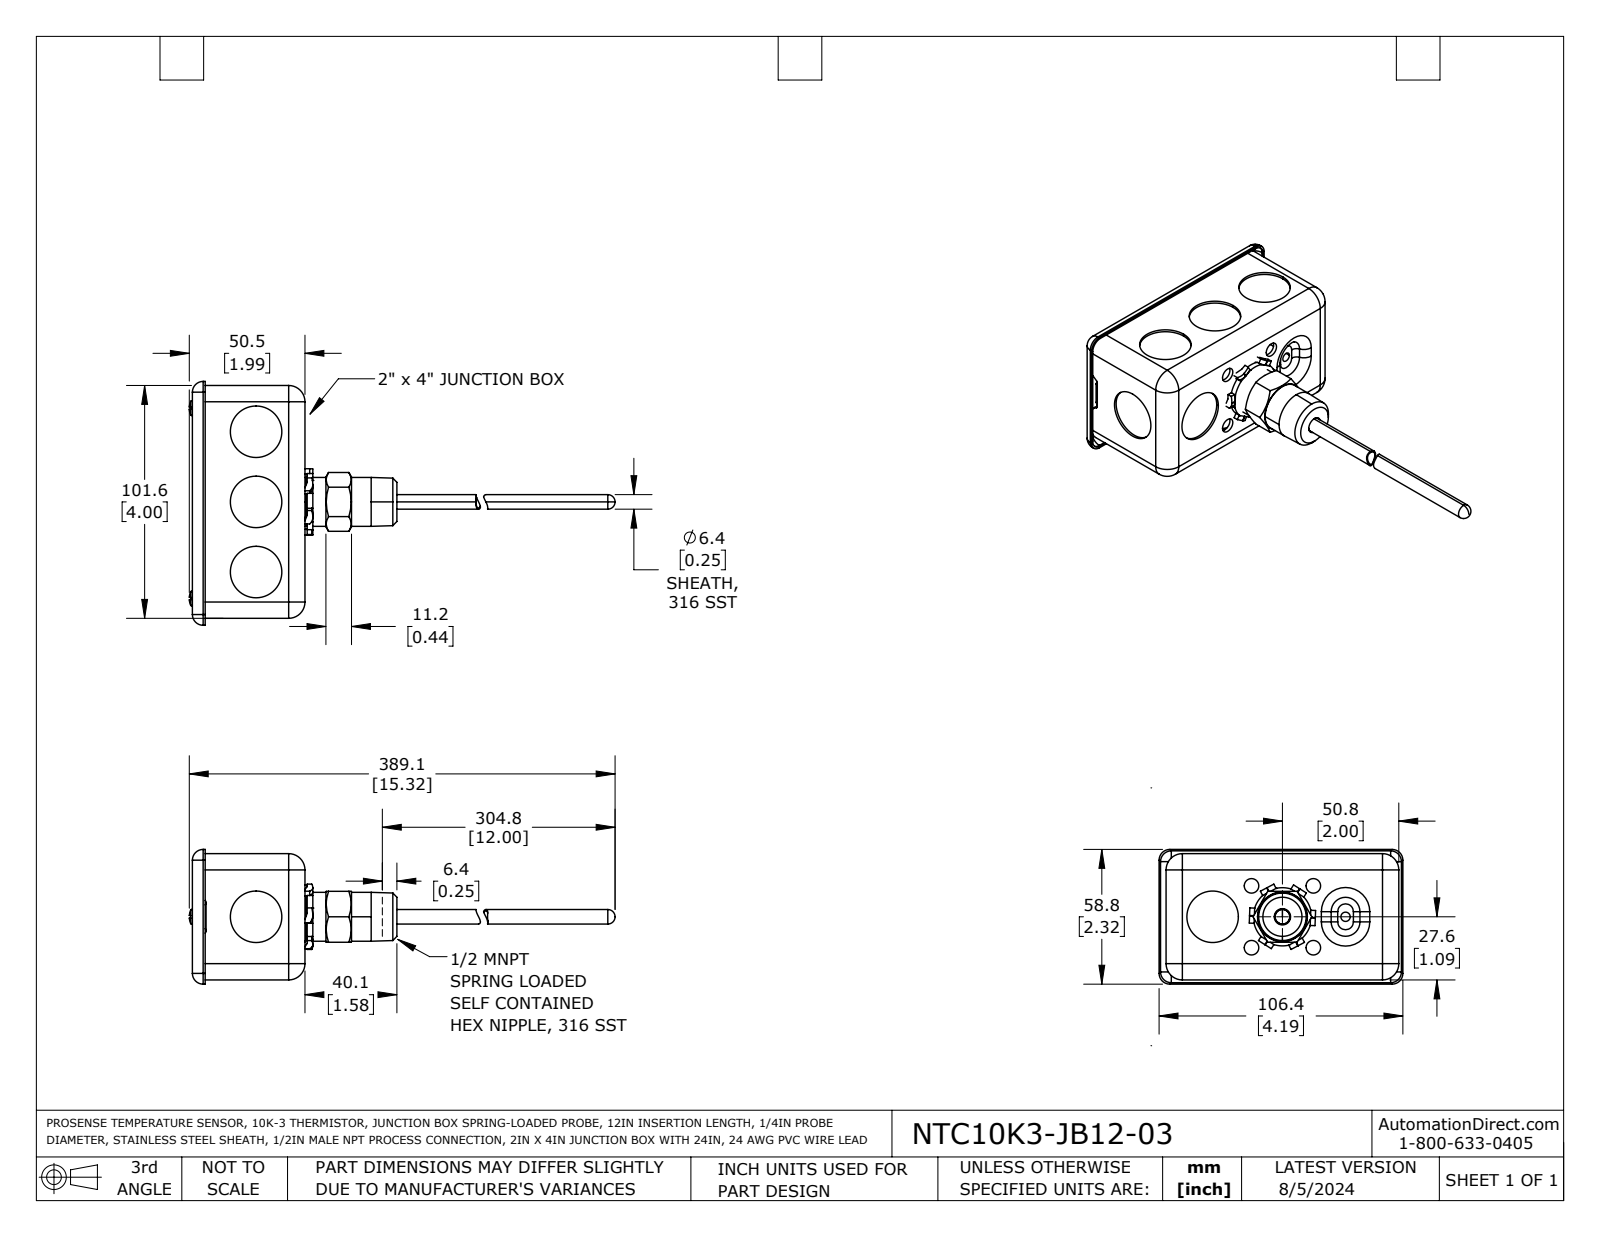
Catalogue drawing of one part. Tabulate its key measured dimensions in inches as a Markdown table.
| quantity | value |
| --- | --- |
| part name | NTC10K3-JB12-03 |
| STEP written by | SolidWorks 2021 (AUTOMOTIVE_DESIGN) |
| units | inches |
| bodies | 5 solids, 366 faces (155 planar, 147 cylindrical, 64 other) |
| overall size | 15.313 × 4.19 × 2.315 |
| volume | 3.194 in³ |
| surface area | 110 in² |
| round holes (diameter × count) | 0.885 × 6, 0.25 × 4, 0.115 × 2, 0.16 × 1, 0.21 × 1, 0.26 × 1, 0.438 × 1, 0.466 × 1 |
| round bosses / shafts (diameter × count) | 0.136 × 2, 0.84 × 1, 0.25 × 1 |
| partial cylindrical surfaces (radius × count) | 0.185 × 16, 0.245 × 8, 0.28 × 8, 0.174 × 6, 0.555 × 6, 0.045 × 4, 0.165 × 4, 0.07 × 2 |
| main face-to-face distances | 0.07, 0.03, 2.03, 2.1, 0.04, 0.1, 0.06, 1.855, 2.07, 2 |
| hole center spacings | 0.751, 1.062, 1.248, 2.254, 0.767, 0.854, 1.205, 1.502 |
